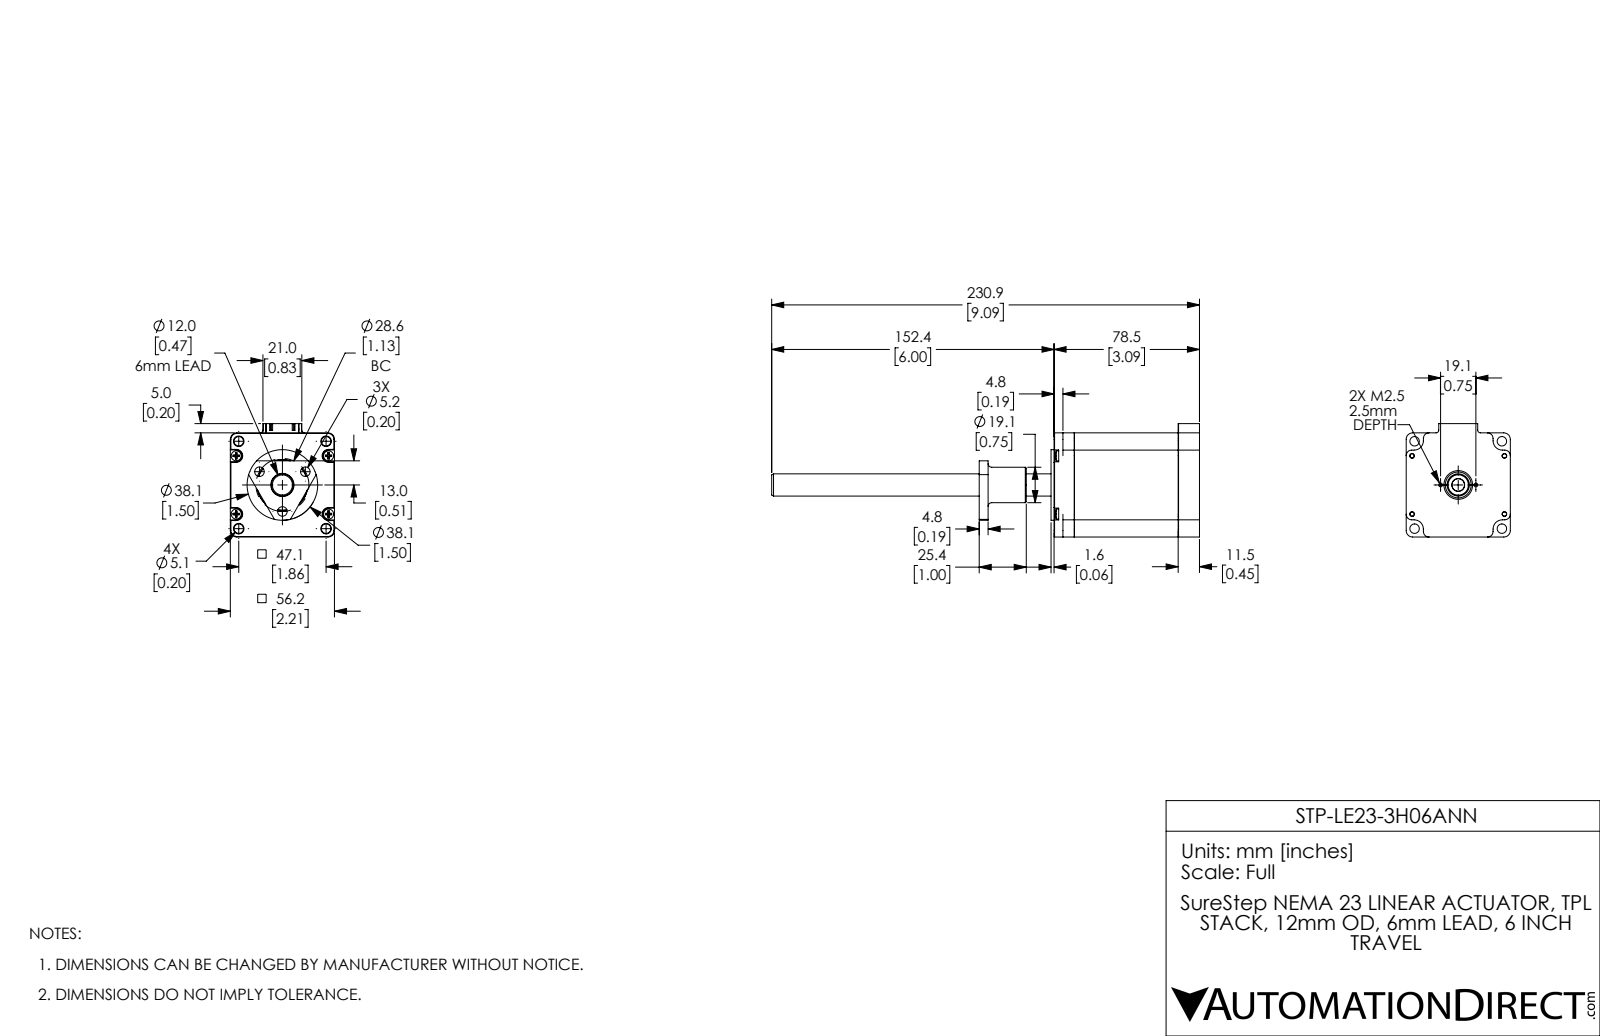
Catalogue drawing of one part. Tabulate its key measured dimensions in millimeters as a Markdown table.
| quantity | value |
| --- | --- |
| part name | STP-LE23-3H06ANN; STP-LE23-3H06ANN_2; STP-LE23-3H06ANN_1 |
| STEP written by | SolidWorks 2017 (AUTOMOTIVE_DESIGN) |
| units | millimeters |
| bodies | 7 solids, 987 faces (376 planar, 452 cylindrical, 159 other) |
| overall size | 230.9 × 61.2 × 56.2 |
| volume | 224 846 mm³ |
| surface area | 62 509 mm² |
| round holes (diameter × count) | 4.5 × 8, 2.5 × 4, 3.3 × 4, 5.1 × 4, 5.16 × 3, 2 × 2, 2.05 × 2, 6.9 × 1, 10.5 × 1, 14.8 × 1, 15.5 × 1, 16 × 1 |
| round bosses / shafts (diameter × count) | 5.4 × 4, 2.91 × 4, 38.1 × 1, 36 × 1, 35.6 × 1, 34.85 × 1, 28 × 1, 19.1 × 1 |
| partial cylindrical surfaces (radius × count) | 1.5 × 10, 0.2 × 8, 3 × 8, 1.8 × 4, 3.2 × 4, 3.5 × 4, 5 × 4, 0.6 × 1 |
| main face-to-face distances | 56.2, 56, 11.5, 67.5, 78.5, 11, 51.4, 67, 1.6, 1.1 |
| hole center spacings | 24.75, 14.12, 33.05, 35.01, 45.74, 48.53, 56.99, 6.55 |
